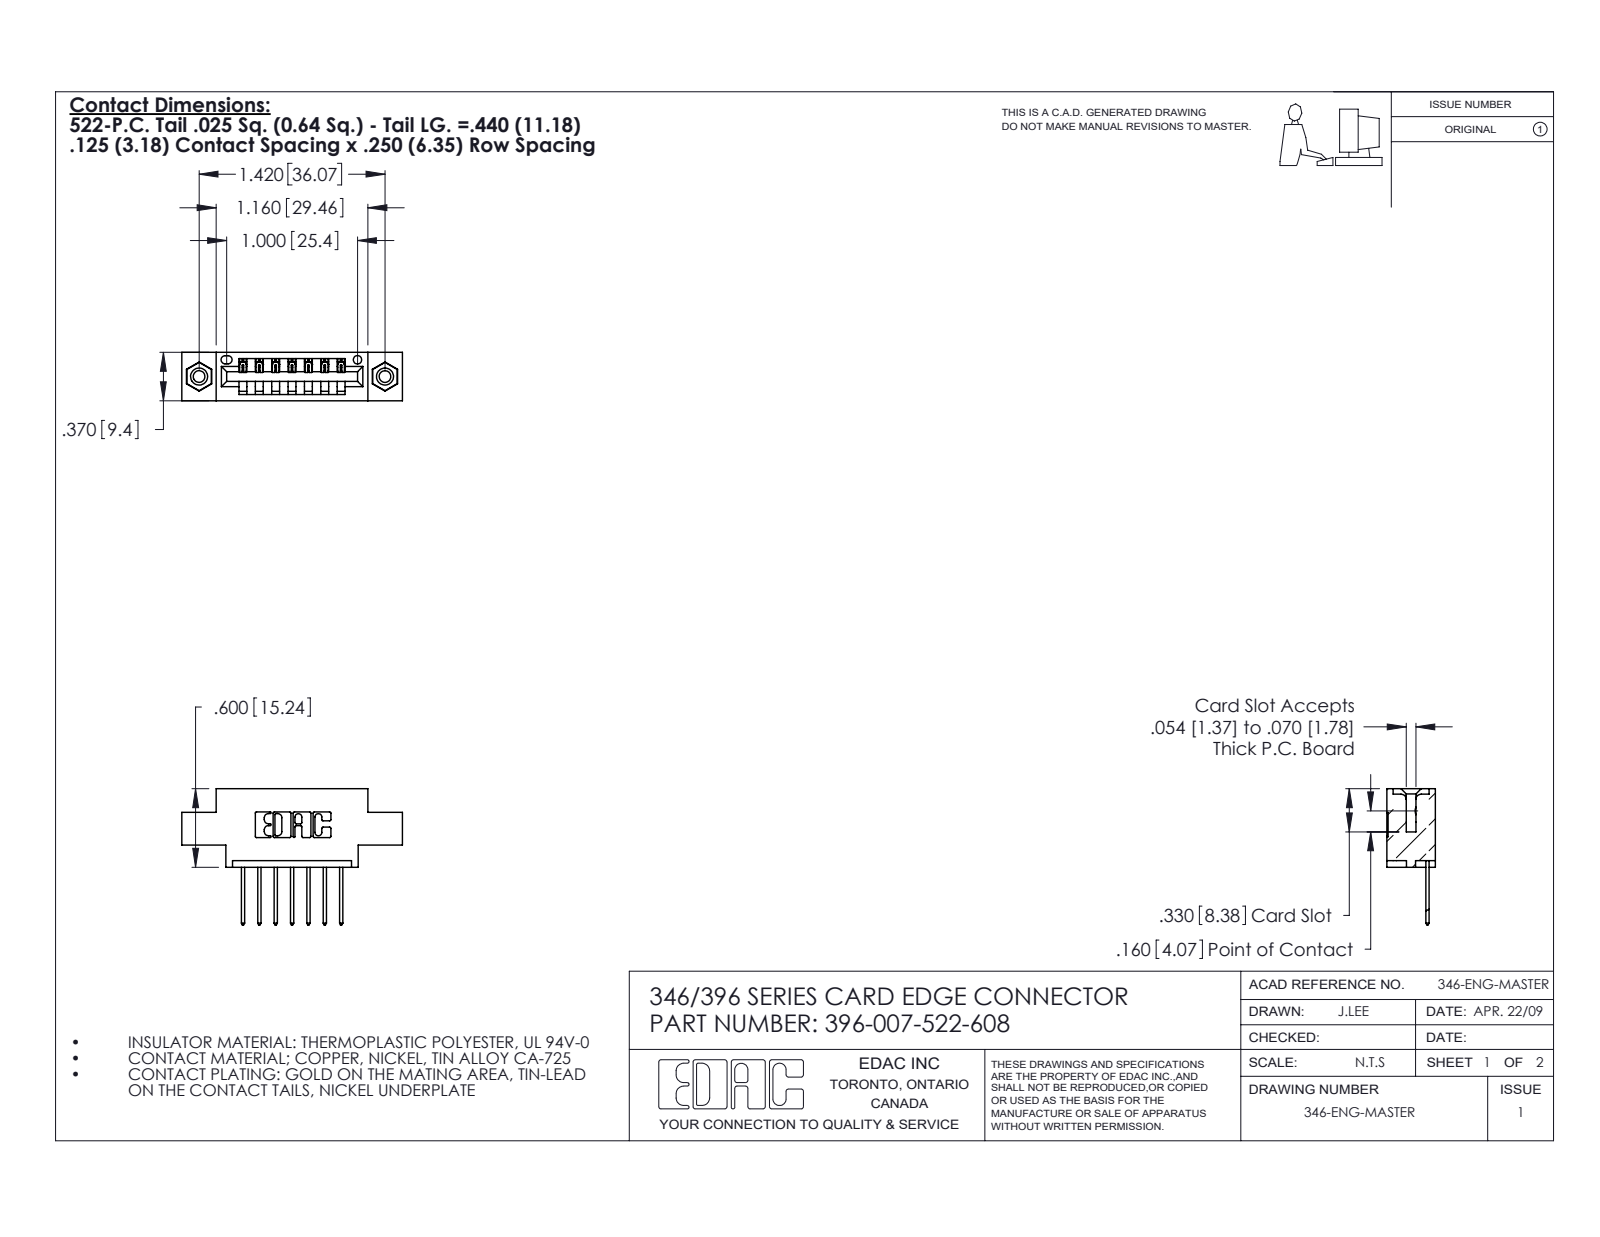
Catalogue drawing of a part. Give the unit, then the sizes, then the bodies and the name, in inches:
Units: inches
Overall size (bounding box): 1.685 × 1.04 × 0.37
Round holes (diameter × count): ⌀0.089 ×2, ⌀0.125 ×2, ⌀0.156 ×2, ⌀0.064 ×1
Round bosses / shafts (diameter × count): ⌀0.155 ×2
Partial cylindrical surfaces — rounded edges, fillets, slot ends (radius × count): R0.01 ×22, R0.006 ×14, R0.01 ×14, R0.007 ×6, R0.031 ×6, R0.026 ×3, R0.031 ×2, R0.04 ×2
Main face-to-face distances: 0.25, 0.37, 0.048, 0.322, 0.222, 0.148, 0.072, 0.298, 0.025, 0.1
Hole centre spacings: 0.246, 1.217, 1.42
Volume: 0.226 in³ · Surface area: 6.896 in²
Bodies: 10 solids, 592 faces (392 planar, 184 cylindrical, 16 other)
Part name (STEP PRODUCT): 346 Part_0.170 Offset - 0.156 Dia-TI; 345-250-001_345-250-003-102; 396-007-522-608; 345-292-001_345-293-122
STEP written by: SolidWorks 2020 (CONFIG_CONTROL_DESIGN)
